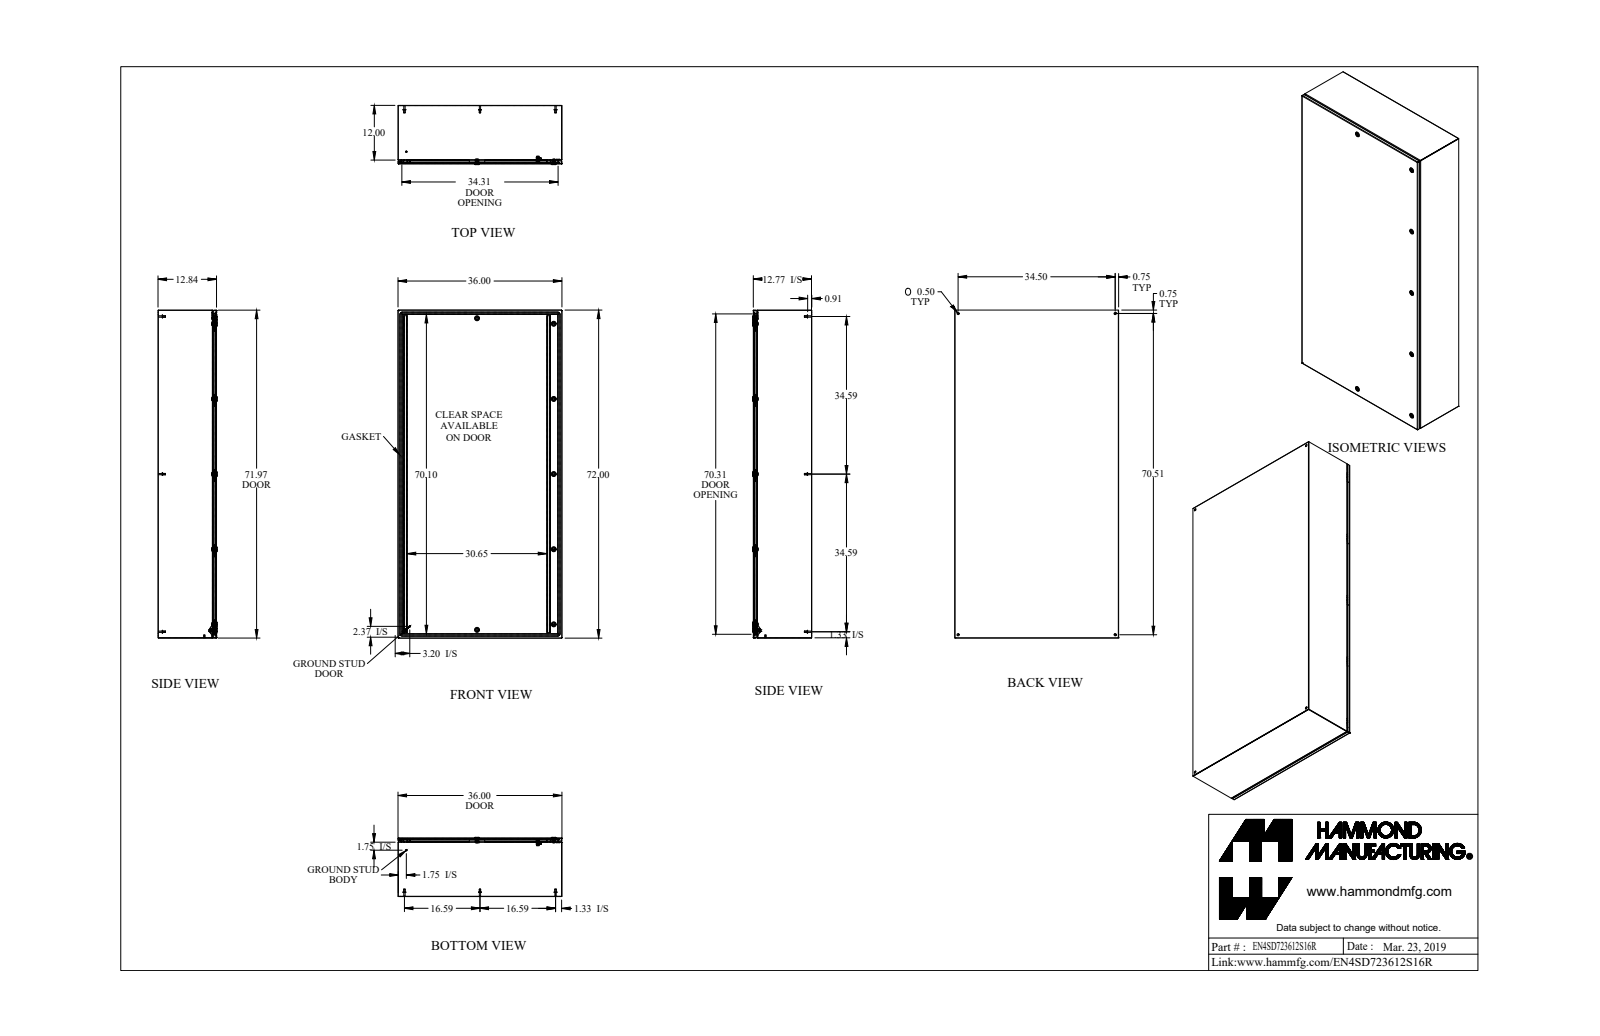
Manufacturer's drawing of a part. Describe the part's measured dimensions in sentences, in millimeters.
The part is named "EN4SD723612S16R". Its 3-D file was written by "SolidWorks 2018 (AUTOMOTIVE_DESIGN)". It is 81 solids with 2027 faces: 1092 planar, 634 cylindrical and 301 other. Overall it measures 1828.8 by 914.4 by 330.2 millimeters. Its volume is 10 450 000 cubic millimeters and its surface area 11 680 000 square millimeters. Round holes: 11 of diameter 12.7, 7 of diameter 5, 7 of diameter 9.8, 7 of diameter 16, 7 of diameter 19.5, 1 of diameter 4.4, 1 of diameter 5, 1 of diameter 6.1, 1 of diameter 6.1, 1 of diameter 7, 1 of diameter 9.5. Round bosses or shafts: 11 of diameter 15.9, 10 of diameter 8, 8 of diameter 7, 7 of diameter 27.9, 7 of diameter 6, 5 of diameter 19.9, 5 of diameter 15.9, 5 of diameter 13.3. Partial cylindrical surfaces (rounded edges, fillets, slot ends): 24 of radius 1.1, 19 of radius 1.6, 17 of radius 0.9, 17 of radius 2.7, 14 of radius 3.2, 10 of radius 0.2, 10 of radius 2.4, 9 of radius 0.4. The main face-to-face distances are 1.8, 324.3, 322.5, 326.2, 912.6, 910.7, 914.4, 1827, 1825.1, 1828.8. The hole center spacings are 837.8, 418.9, 418.9, 422.5, 428.8, 455.4, 851.3, 876.3.
